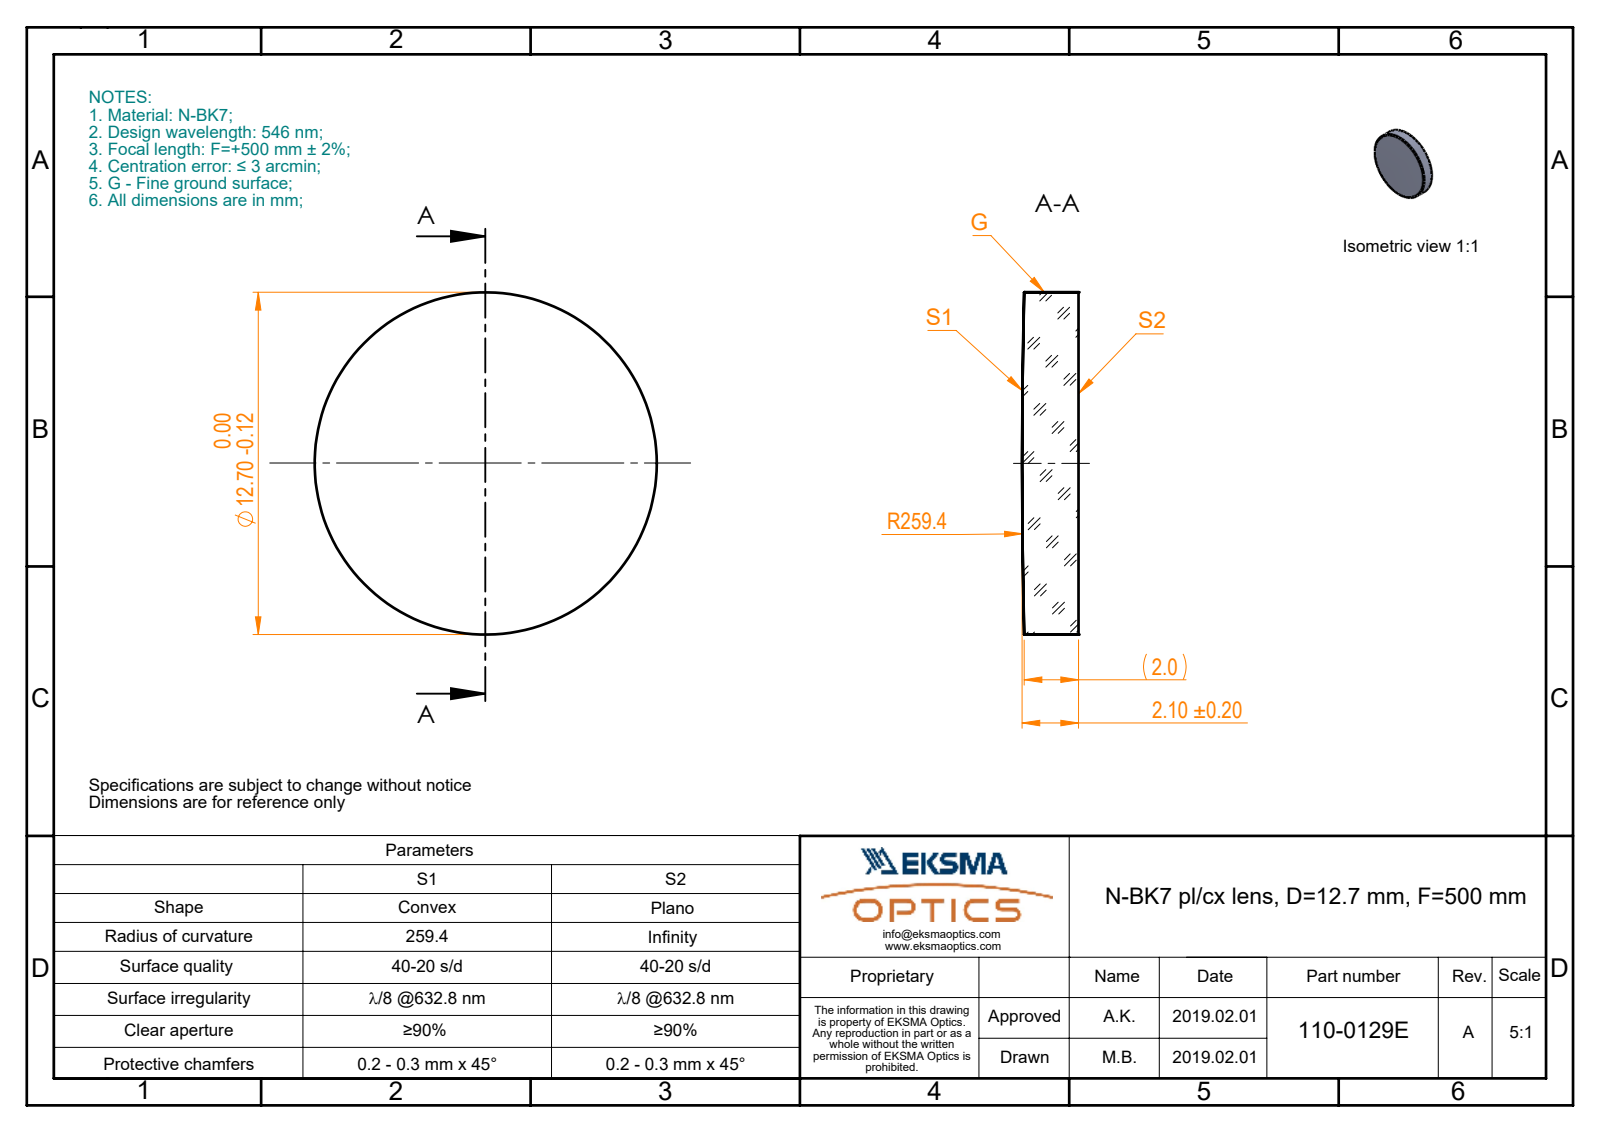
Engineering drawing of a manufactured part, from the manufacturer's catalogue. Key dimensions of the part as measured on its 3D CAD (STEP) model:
Part name (STEP PRODUCT): 110-0129E BK7 pl-cx 12.7 F500
STEP written by: SolidWorks 2017 (CONFIG_CONTROL_DESIGN)
Units: millimetres
Bodies: 1 solid, 5 faces (1 planar, 2 cylindrical, 2 other)
Overall size (bounding box): 12.7 × 12.7 × 2.1
Volume: 261 mm³ · Surface area: 334 mm²
Round bosses / shafts (diameter × count): ⌀12.7 ×1
